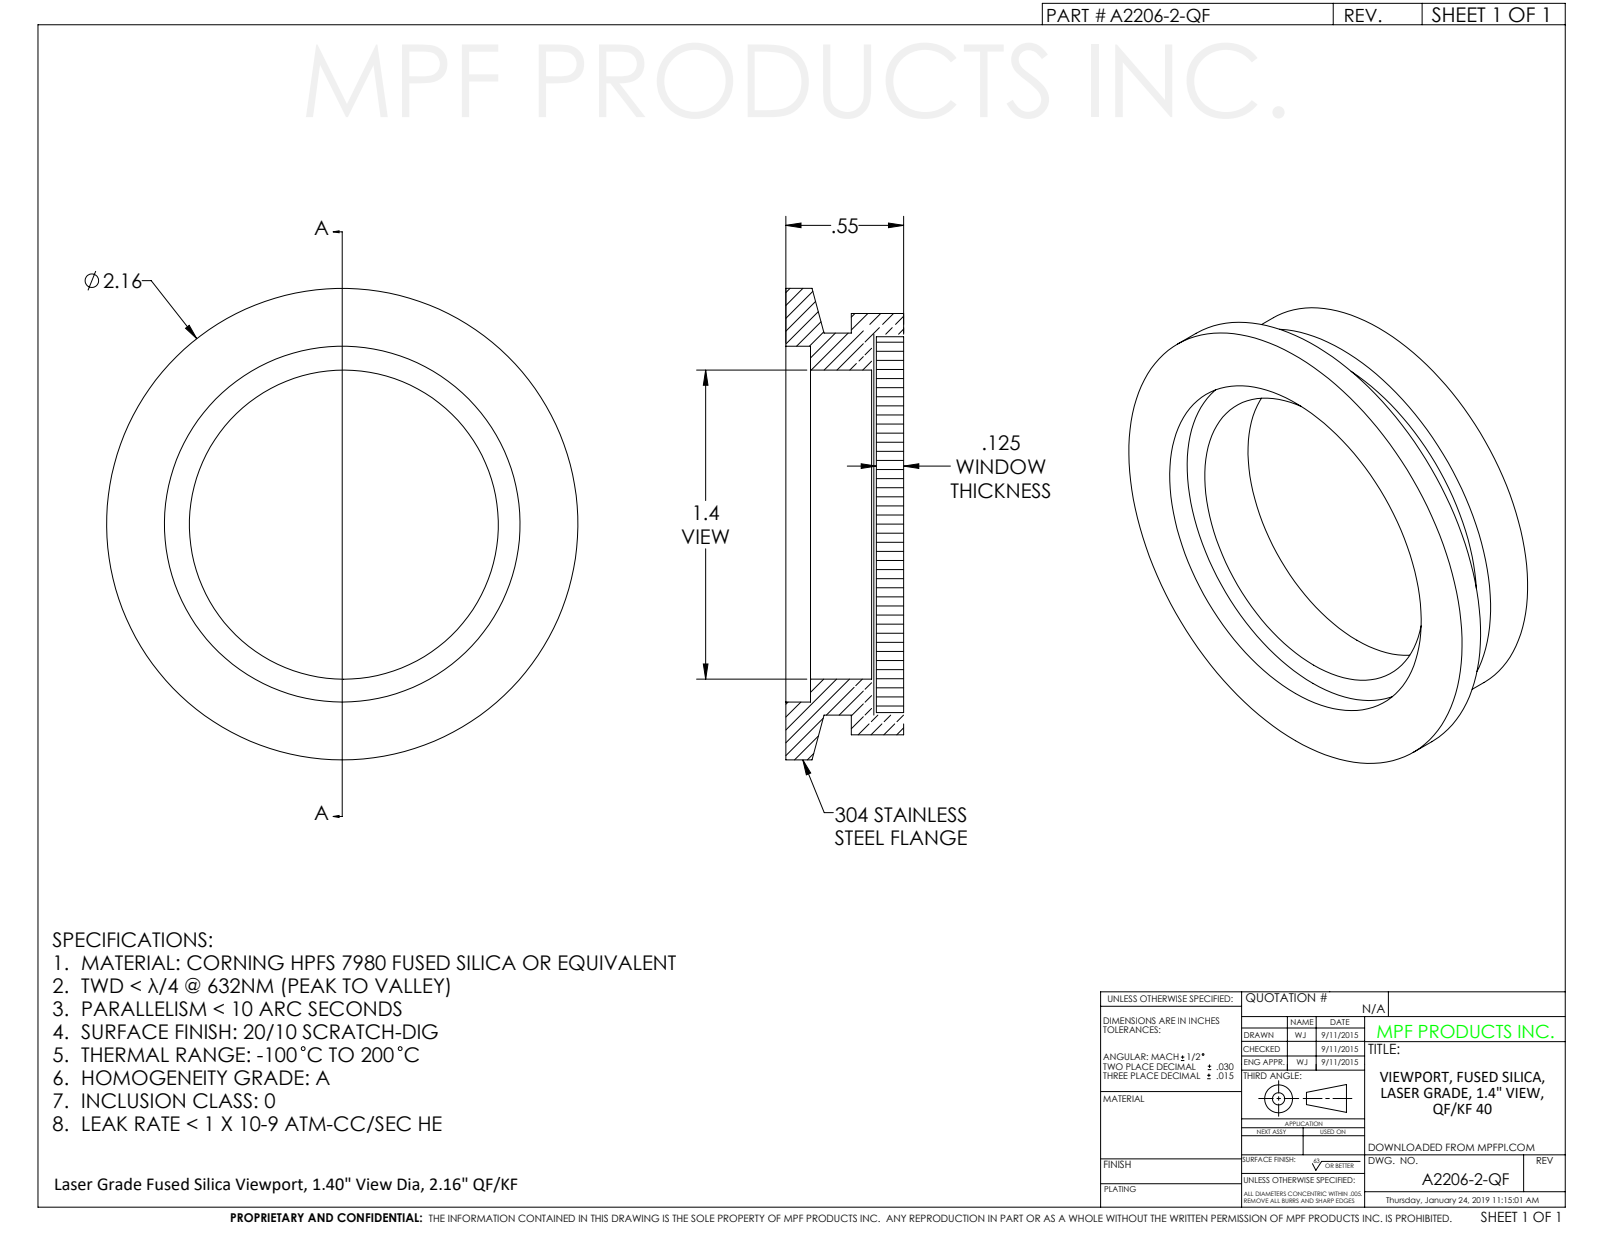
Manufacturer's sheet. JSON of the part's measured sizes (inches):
{"part_name": "A2206-2-QF", "step_written_by": "SolidWorks 2011 (CONFIG_CONTROL_DESIGN)", "units": "inches", "bodies": {"solids": 1, "faces": 55, "planar": 13, "cylindrical": 28, "other": 14}, "overall_size": [2.16, 2.16, 0.54], "volume_in3": 0.781, "surface_area_in2": 19.15, "round_holes": [[1.42, 1], [1.473, 1], [1.495, 1], [1.63, 1], [1.745, 1], [1.83, 1]], "round_bosses_or_shafts": [[2.16, 1], [1.93, 1], [1.765, 1], [1.75, 1], [1.747, 1], [1.464, 1], [1.44, 1]], "partial_cylinders_radius": [[0.71, 1]], "face_to_face_distances": [0.125, 0.398, 0.523, 0.098, 0.3, 0.223, 0.128, 0.172, 0.27, 0.395]}
